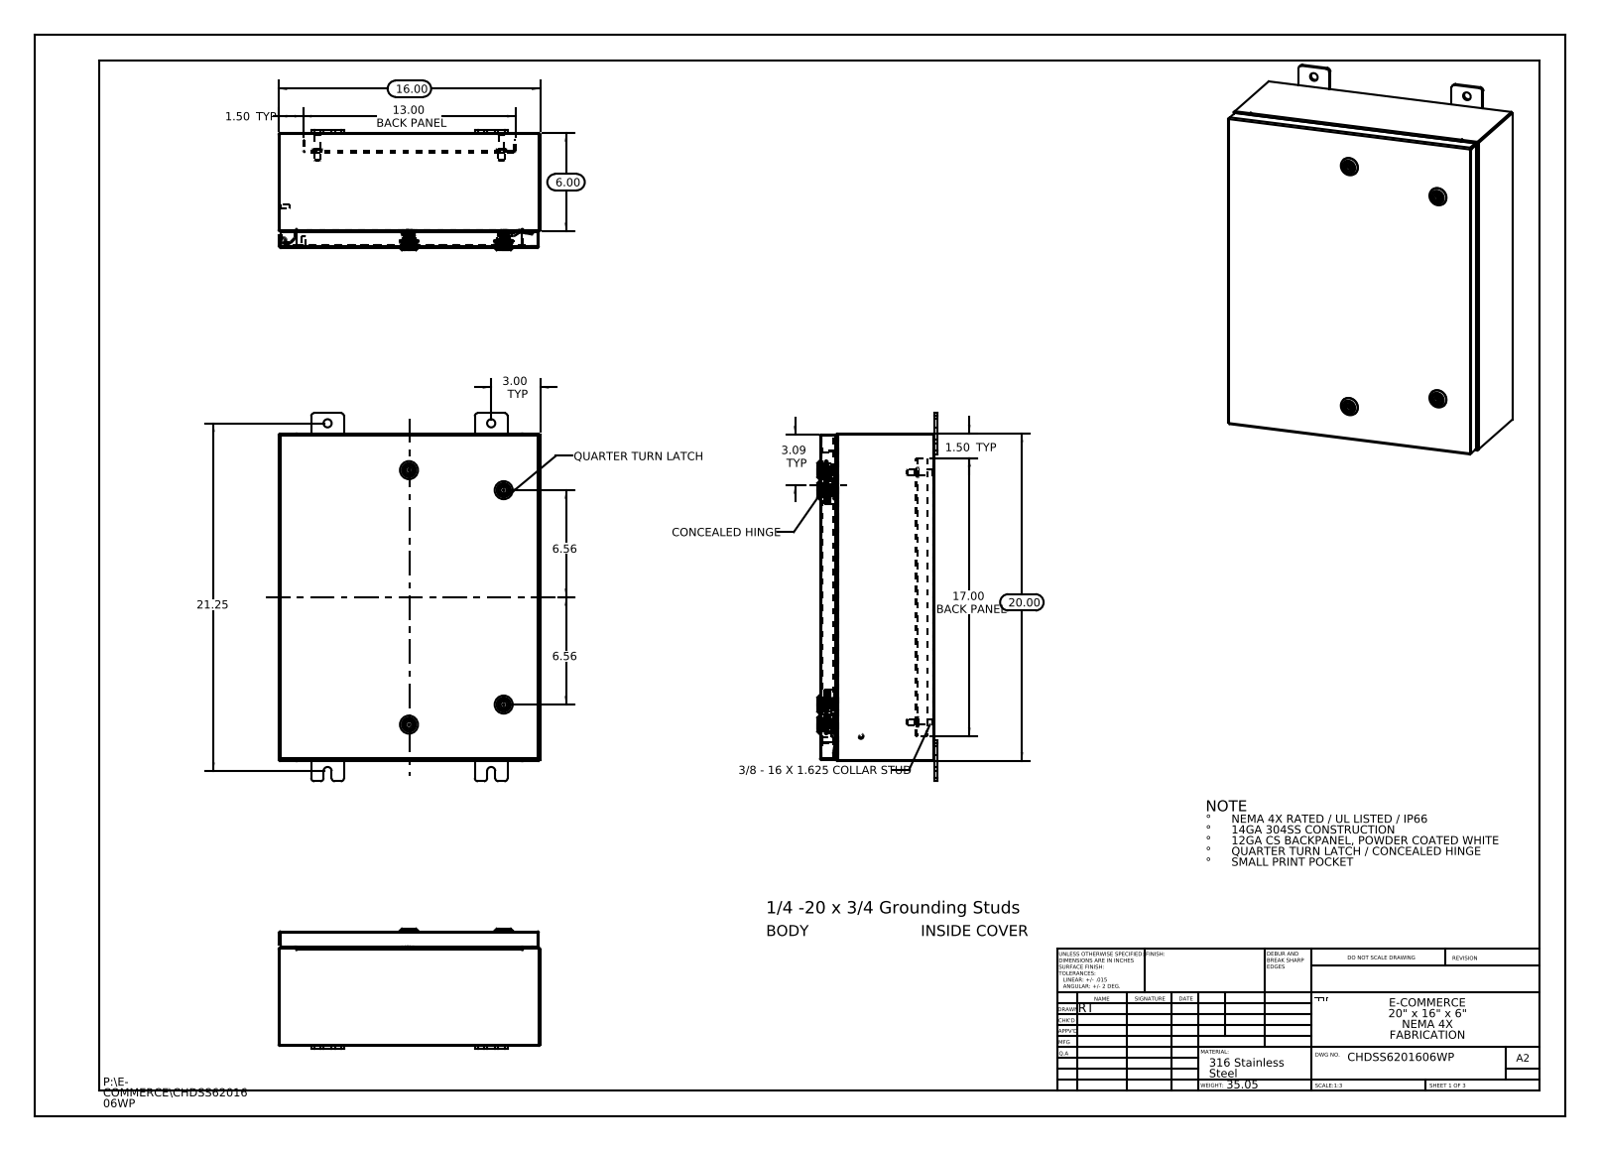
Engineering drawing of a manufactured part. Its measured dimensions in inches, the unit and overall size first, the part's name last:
Units: inches
Overall size (bounding box): 22.5 × 16 × 7.356
Round holes (diameter × count): ⌀0.5 ×8, ⌀0.136 ×4, ⌀0.197 ×4, ⌀0.394 ×4, ⌀0.4 ×4, ⌀0.63 ×4, ⌀0.787 ×4, ⌀0.211 ×1
Round bosses / shafts (diameter × count): ⌀0.236 ×6, ⌀1.102 ×4, ⌀0.78 ×4, ⌀0.626 ×4, ⌀0.625 ×4, ⌀0.61 ×4, ⌀0.531 ×4, ⌀0.392 ×4
Partial cylindrical surfaces — rounded edges, fillets, slot ends (radius × count): R0.006 ×132, R0.118 ×132, R0.028 ×48, R0.19 ×24, R0.013 ×20, R0.088 ×18, R0.02 ×16, R0.197 ×16
Main face-to-face distances: 0.075, 0.074, 7.01, 6.935, 6.936, 6.861, 0.104, 15.925, 1, 1.075
Hole centre spacings: 0.688, 1.858, 3.065, 5.916, 10, 11.25, 13.687, 15.25
Volume: 125.7 in³ · Surface area: 3 139 in²
Bodies: 43 solids, 3794 faces (1164 planar, 1186 cylindrical, 1444 other)
Part name (STEP PRODUCT): CHDSS6201606WP Body; Concealed Hinge (Cover Side); Quarter-20 CD Stud; Housing-211301-IB-Industrilas_Housing-211301-IB-Industrilas (+8 more)
STEP written by: SolidWorks 2013 (CONFIG_CONTROL_DESIGN)
